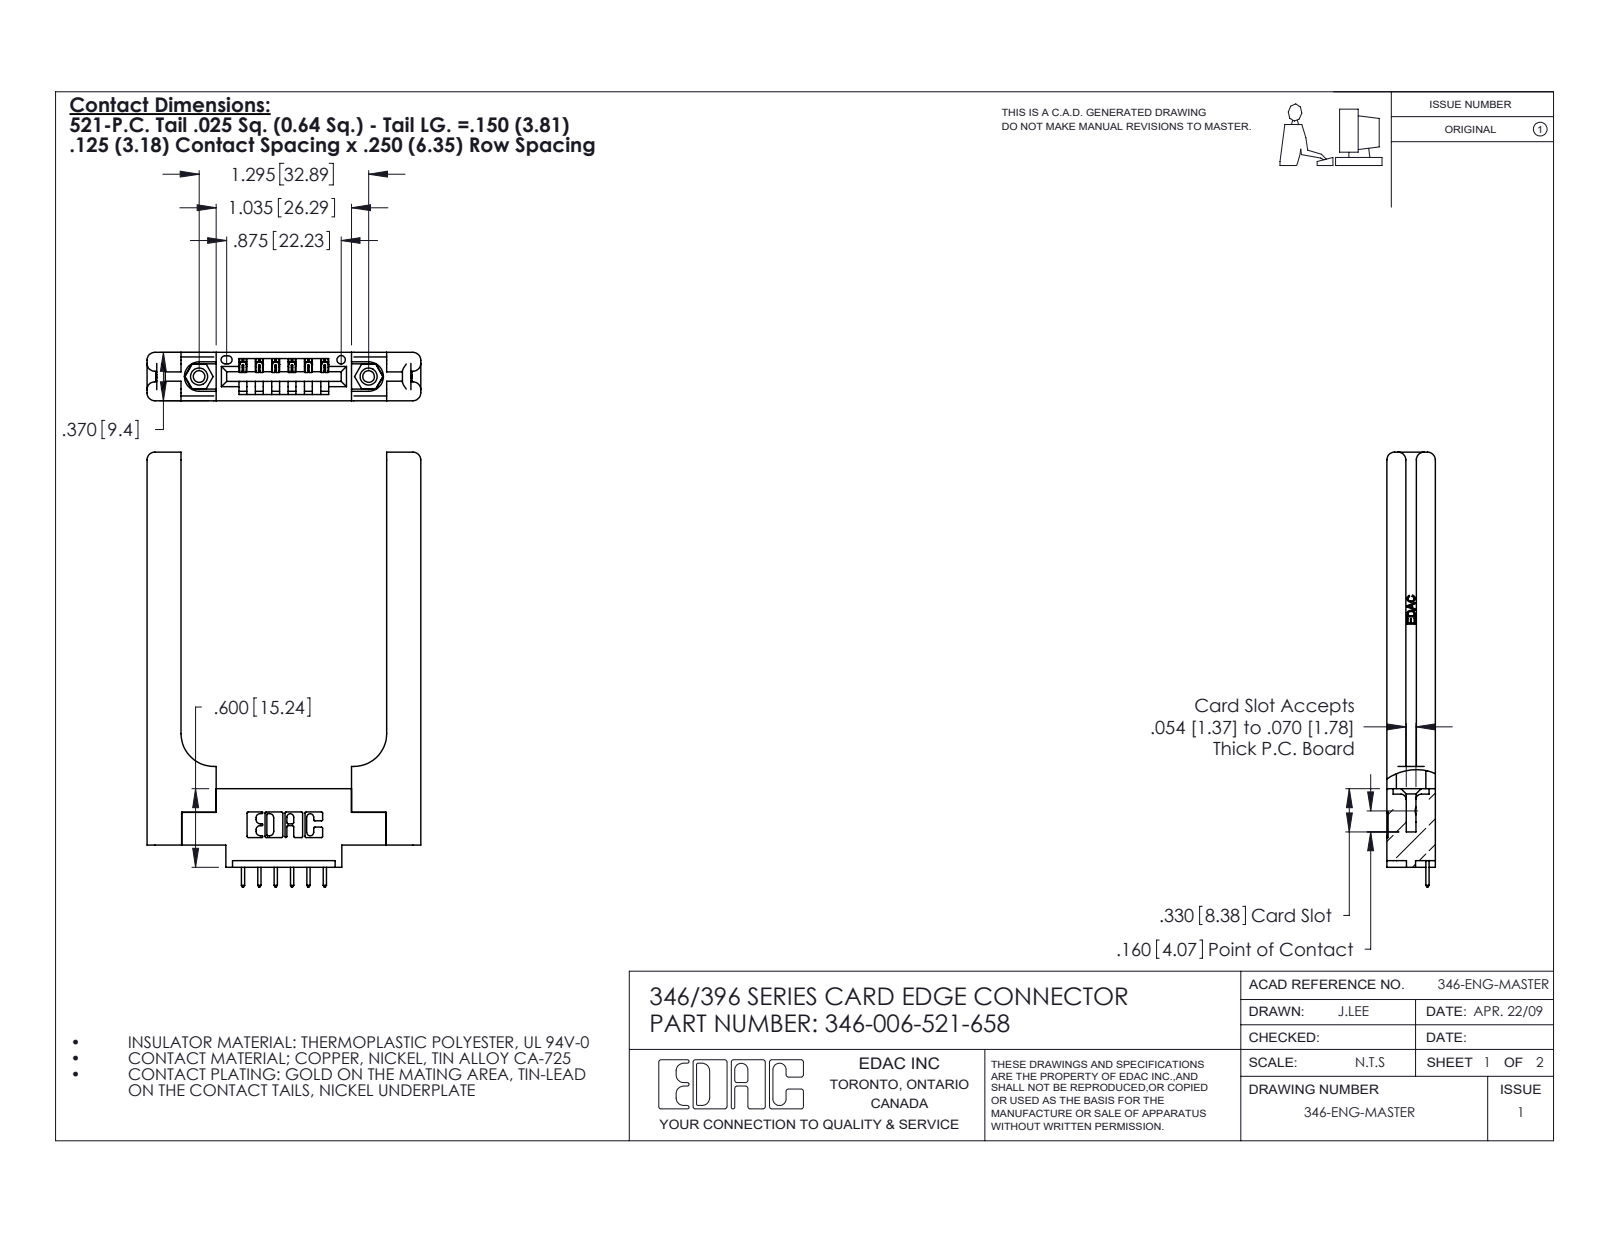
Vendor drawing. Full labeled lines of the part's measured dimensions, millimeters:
Part name (STEP PRODUCT): 346-220-058_345-220-058; 345-250-001_345-250-001-102; 346-006-521-658; 345-292-001_345-293-121 (+1 more)
STEP written by: SolidWorks 2020 (CONFIG_CONTROL_DESIGN)
Units: millimetres
Bodies: 11 solids, 744 faces (482 planar, 202 cylindrical, 60 other)
Overall size (bounding box): 84.3 × 53.1 × 9.4
Volume: 12 200 mm³ · Surface area: 10 710 mm²
Round holes (diameter × count): ⌀2.3 ×2, ⌀3.2 ×2, ⌀4 ×2, ⌀1.6 ×1
Round bosses / shafts (diameter × count): ⌀3.9 ×2
Partial cylindrical surfaces — rounded edges, fillets, slot ends (radius × count): R0.3 ×22, R1.5 ×16, R0.2 ×12, R0.3 ×12, R0.2 ×6, R0.8 ×6, R0.7 ×3, R0.8 ×2
Main face-to-face distances: 9.4, 3.8, 5.6, 1.8, 3.8, 6.4, 39.9, 1.8, 3, 1.2
Hole centre spacings: 6.2, 27.7, 32.9
